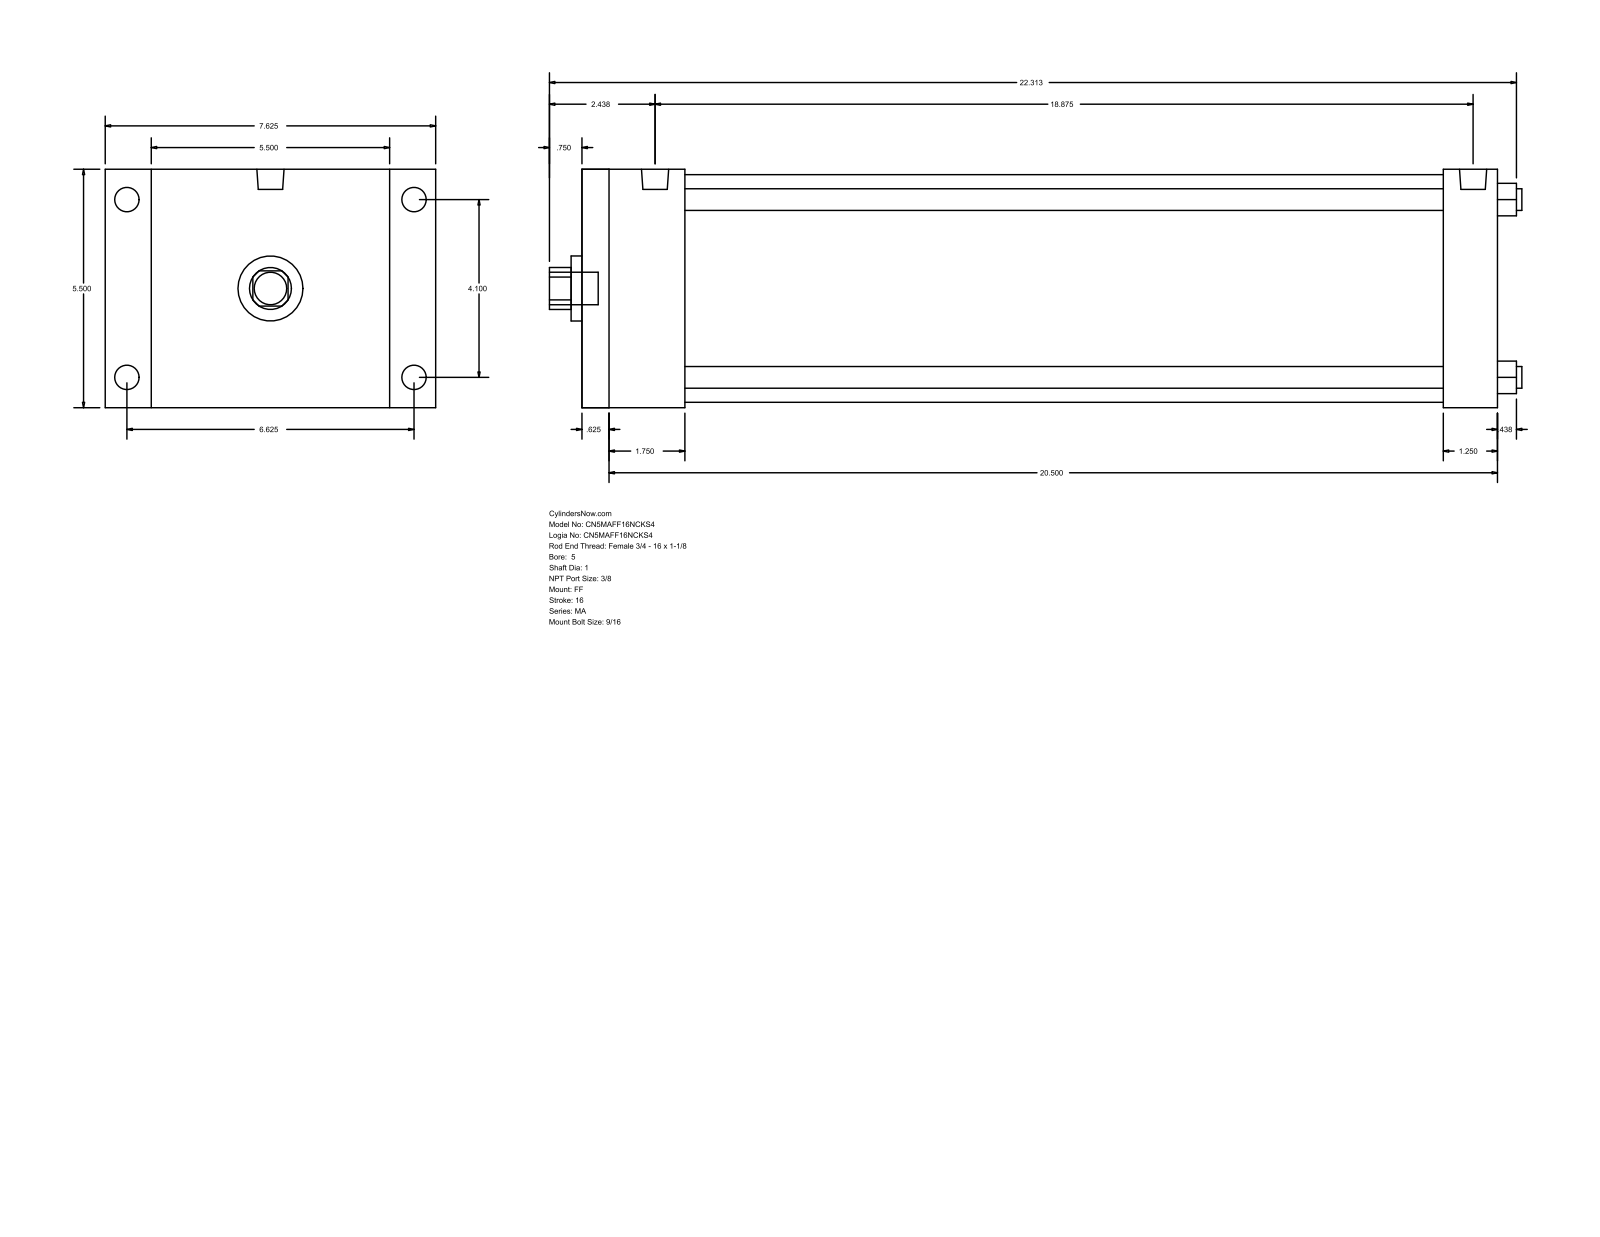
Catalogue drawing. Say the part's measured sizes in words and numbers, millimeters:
The part is named "MA_FF__0500_1". Its 3-D file was written by "GSSL Pune (CONFIG_CONTROL_DESIGN)". It is 0 solids with 92 faces: 64 planar, 28 cylindrical and 0 other. Overall it measures 569.91 by 193.68 by 139.7 millimeters. Round holes: 4 of diameter 12.7, 1 of diameter 25.4, 1 of diameter 38.1, 1 of diameter 133.35. Round bosses or shafts: 4 of diameter 14.29, 4 of diameter 11.11, 2 of diameter 15.93, 1 of diameter 19.05. Partial cylindrical surfaces (rounded edges, fillets, slot ends): 1 of radius 12.29. The main face-to-face distances are 139.7, 536.57, 15.87, 520.7, 504.83, 488.96, 31.74, 60.33, 44.46, 444.5. The hole center spacings are 73.64, 104.14, 147.28.
